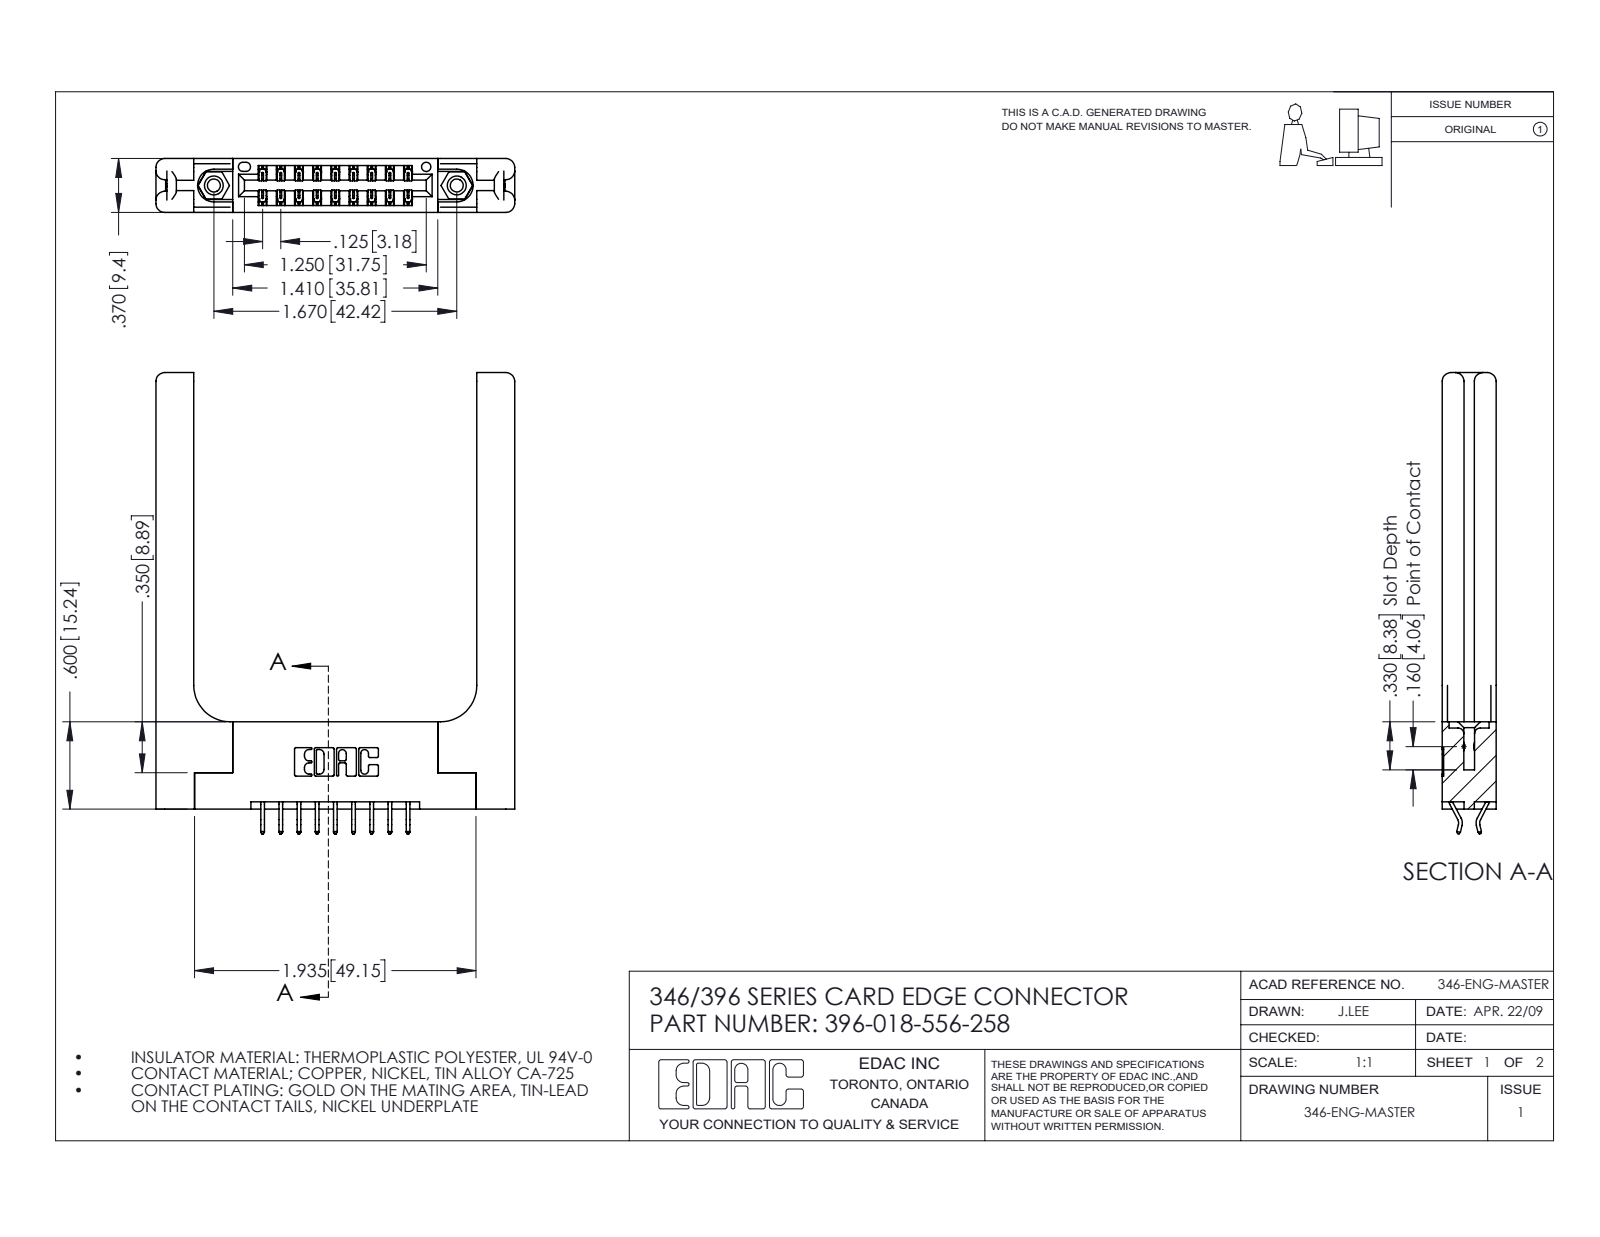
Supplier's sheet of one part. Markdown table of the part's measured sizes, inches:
| quantity | value |
| --- | --- |
| part name | 345-292-001_556 Tail; 346-220-058_345-220-058; 396-018-556-258; 345-250-001_345-250-001-102 (+1 more) |
| STEP written by | SolidWorks 2016 (CONFIG_CONTROL_DESIGN) |
| units | inches |
| bodies | 23 solids, 1422 faces (926 planar, 436 cylindrical, 60 other) |
| overall size | 3.17 × 2.466 × 0.37 |
| volume | 0.814 in³ |
| surface area | 19.34 in² |
| round holes (diameter × count) | 0.089 × 2, 0.125 × 2, 0.156 × 2, 0.064 × 1 |
| round bosses / shafts (diameter × count) | 0.155 × 2 |
| partial cylindrical surfaces (radius × count) | 0.006 × 27, 0.01 × 22, 0.06 × 16, 0.007 × 6, 0.031 × 6, 0.026 × 3, 0.01 × 2, 0.014 × 2 |
| main face-to-face distances | 0.37, 0.15, 0.22, 0.072, 0.148, 0.25, 0.102, 0.048, 0.322, 0.173 |
| hole center spacings | 0.246, 1.465, 1.67 |
